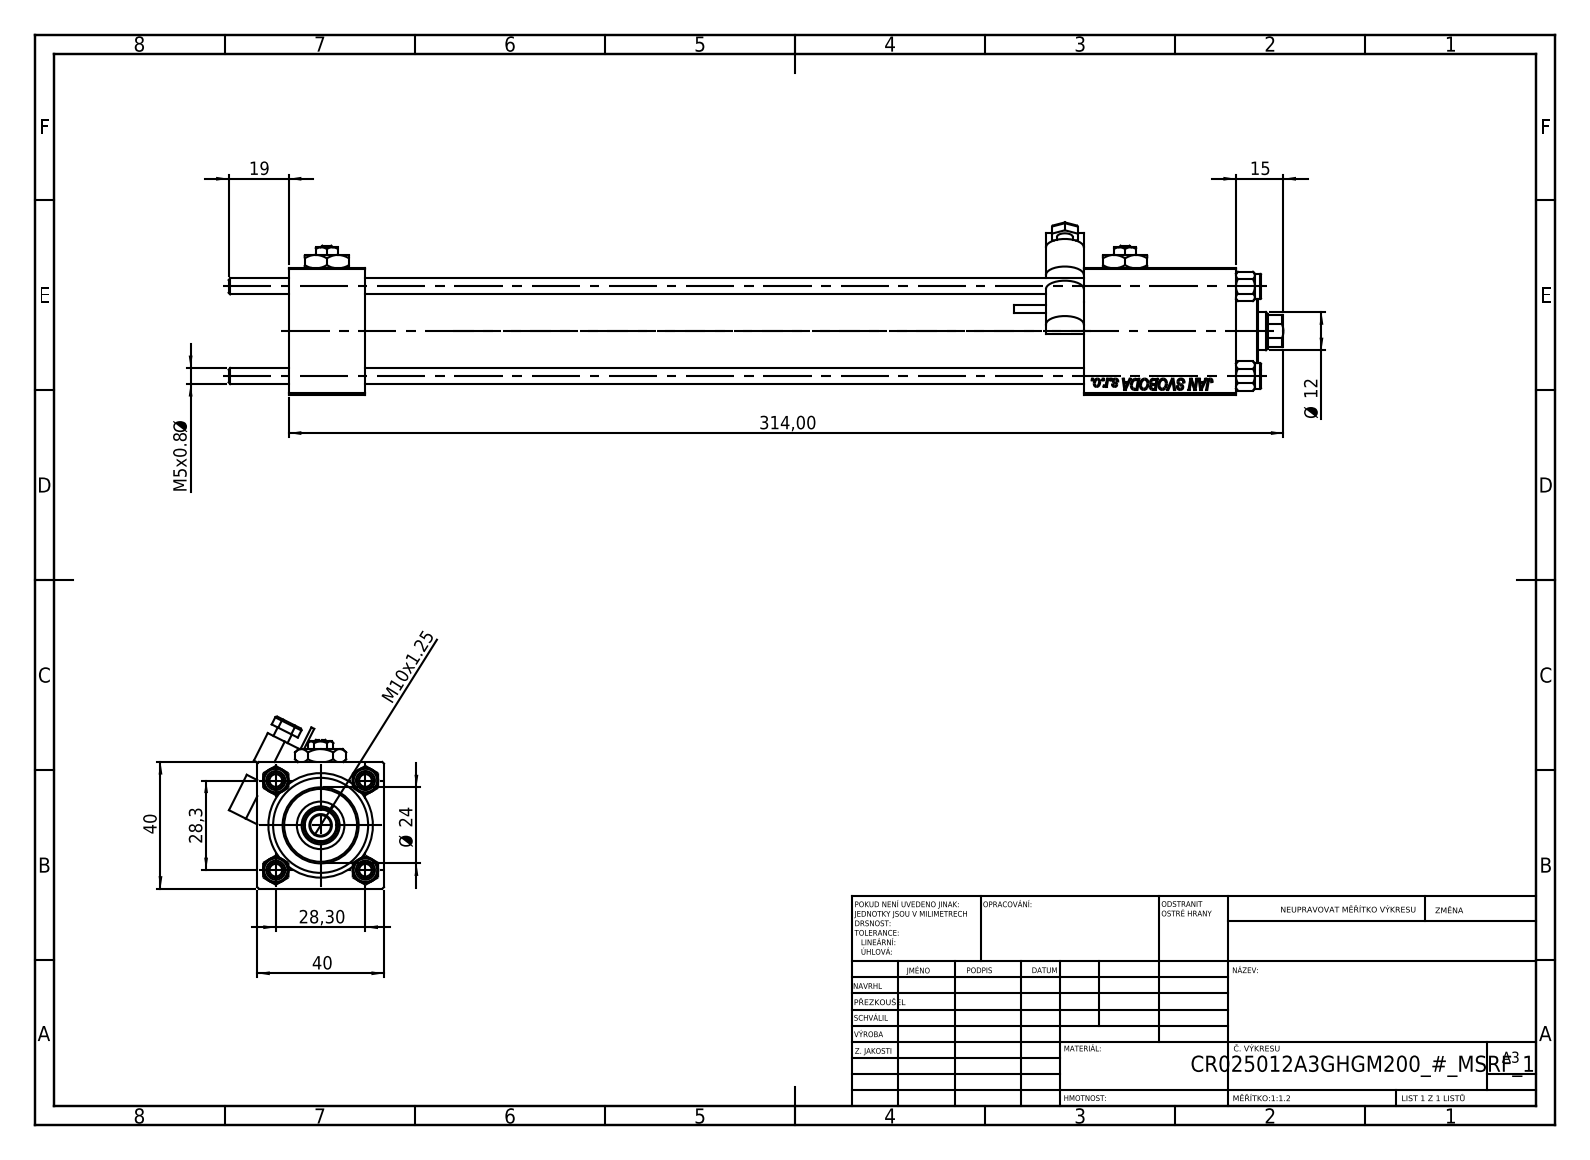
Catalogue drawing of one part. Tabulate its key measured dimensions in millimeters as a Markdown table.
| quantity | value |
| --- | --- |
| part name | V215CR_VCP; V215CR_BODY_A; V215_VC_A; Zatka_pro_OIL_PORT (+3 more) |
| STEP written by | SolidWorks 2019 (CONFIG_CONTROL_DESIGN) |
| units | millimeters |
| bodies | 14 solids, 1264 faces (582 planar, 104 cylindrical, 578 other) |
| overall size | 333 × 54.35 × 48.93 |
| volume | 228 867 mm³ |
| surface area | 112 477 mm² |
| round holes (diameter × count) | 5 × 4, 20 × 3, 7 × 2, 13.16 × 2, 6.5 × 1, 12 × 1, 15 × 1, 25 × 1, 30 × 1 |
| round bosses / shafts (diameter × count) | 8 × 4, 31 × 1, 24 × 1, 5 × 1, 2.5 × 1 |
| partial cylindrical surfaces (radius × count) | 0.5 × 6, 6 × 2, 5.5 × 1 |
| main face-to-face distances | 40, 24, 251, 227, 39.8, 299, 275, 48, 270.3, 246.3 |
| hole center spacings | 20.01, 28.3, 40.02, 252 |
